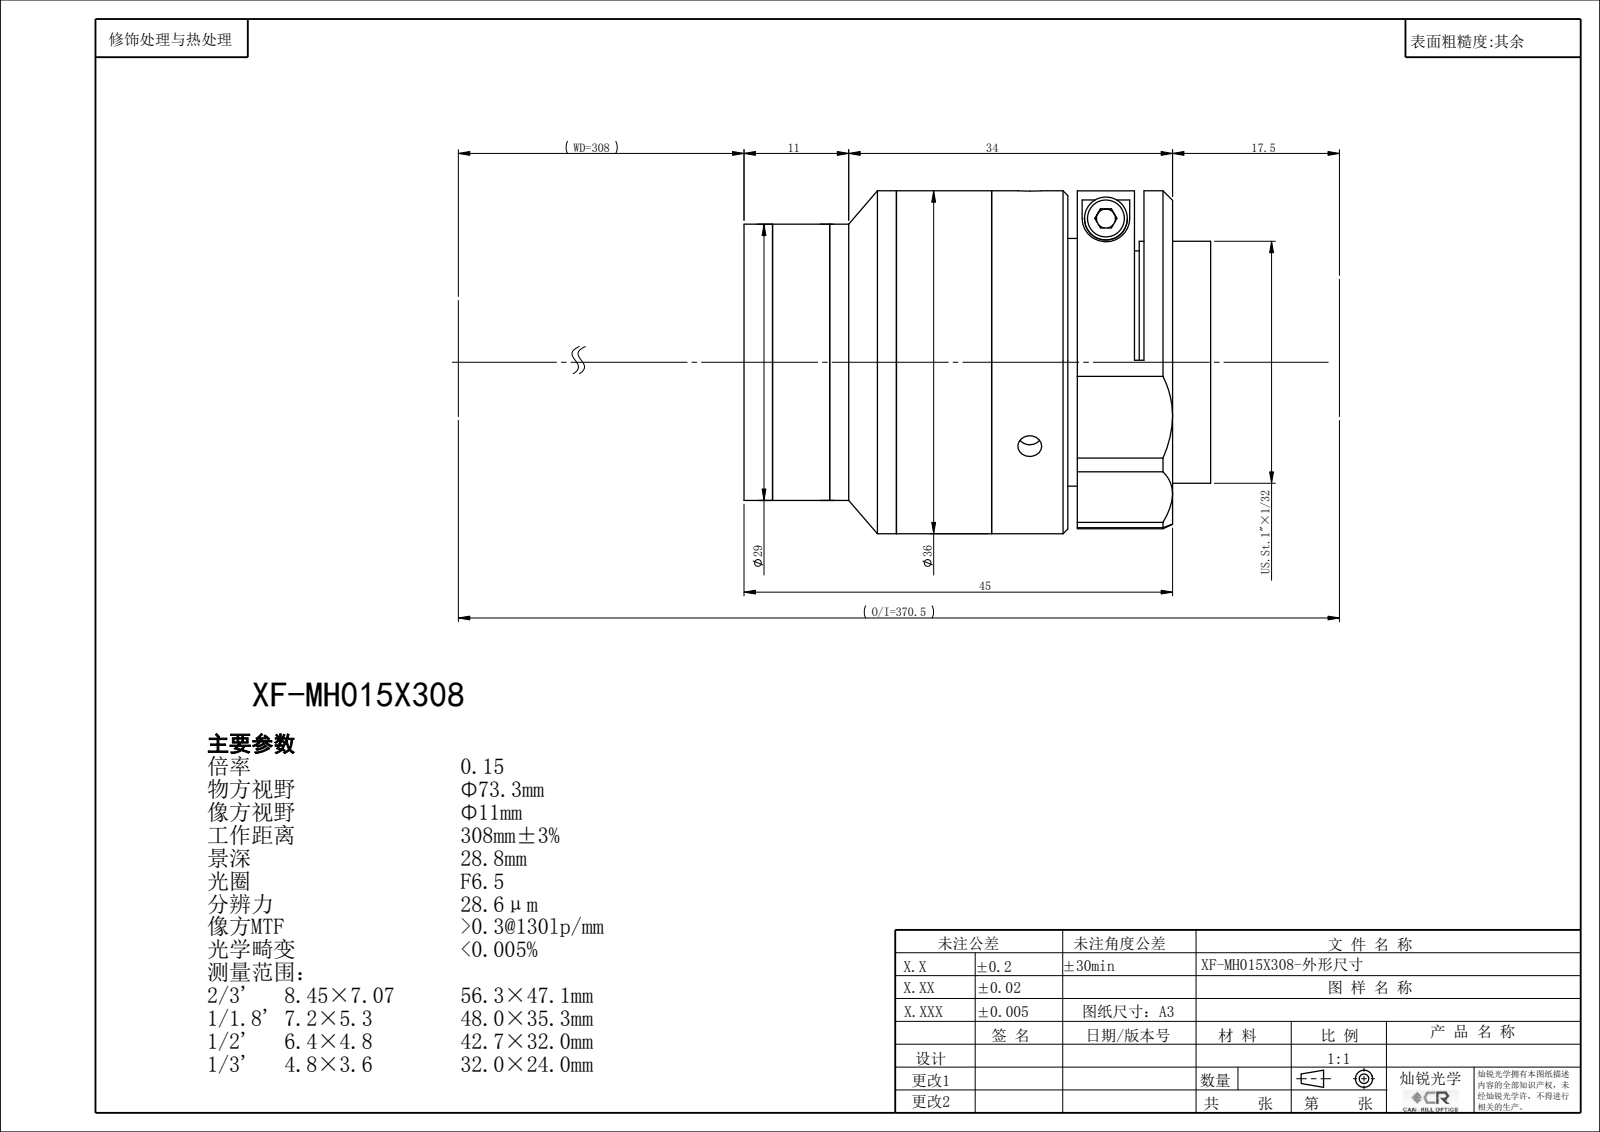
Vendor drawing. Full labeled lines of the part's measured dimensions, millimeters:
Part name (STEP PRODUCT): XF-MH015X308
STEP written by: SolidWorks 2022 (CONFIG_CONTROL_DESIGN)
Units: millimetres
Bodies: 0 solids, 125 faces (63 planar, 40 cylindrical, 22 other)
Overall size (bounding box): 49.1 × 36.01 × 36
Round holes (diameter × count): ⌀2.5 ×3, ⌀14 ×1, ⌀22.4 ×1, ⌀24 ×1, ⌀24.9 ×1, ⌀26.4 ×1, ⌀27 ×1
Round bosses / shafts (diameter × count): ⌀36 ×1, ⌀34 ×1, ⌀29 ×1, ⌀25.4 ×1
Main face-to-face distances: 19.08, 22.22, 41.3, 1.5, 39.8, 17.58, 12.22, 10, 27.58, 29.08
